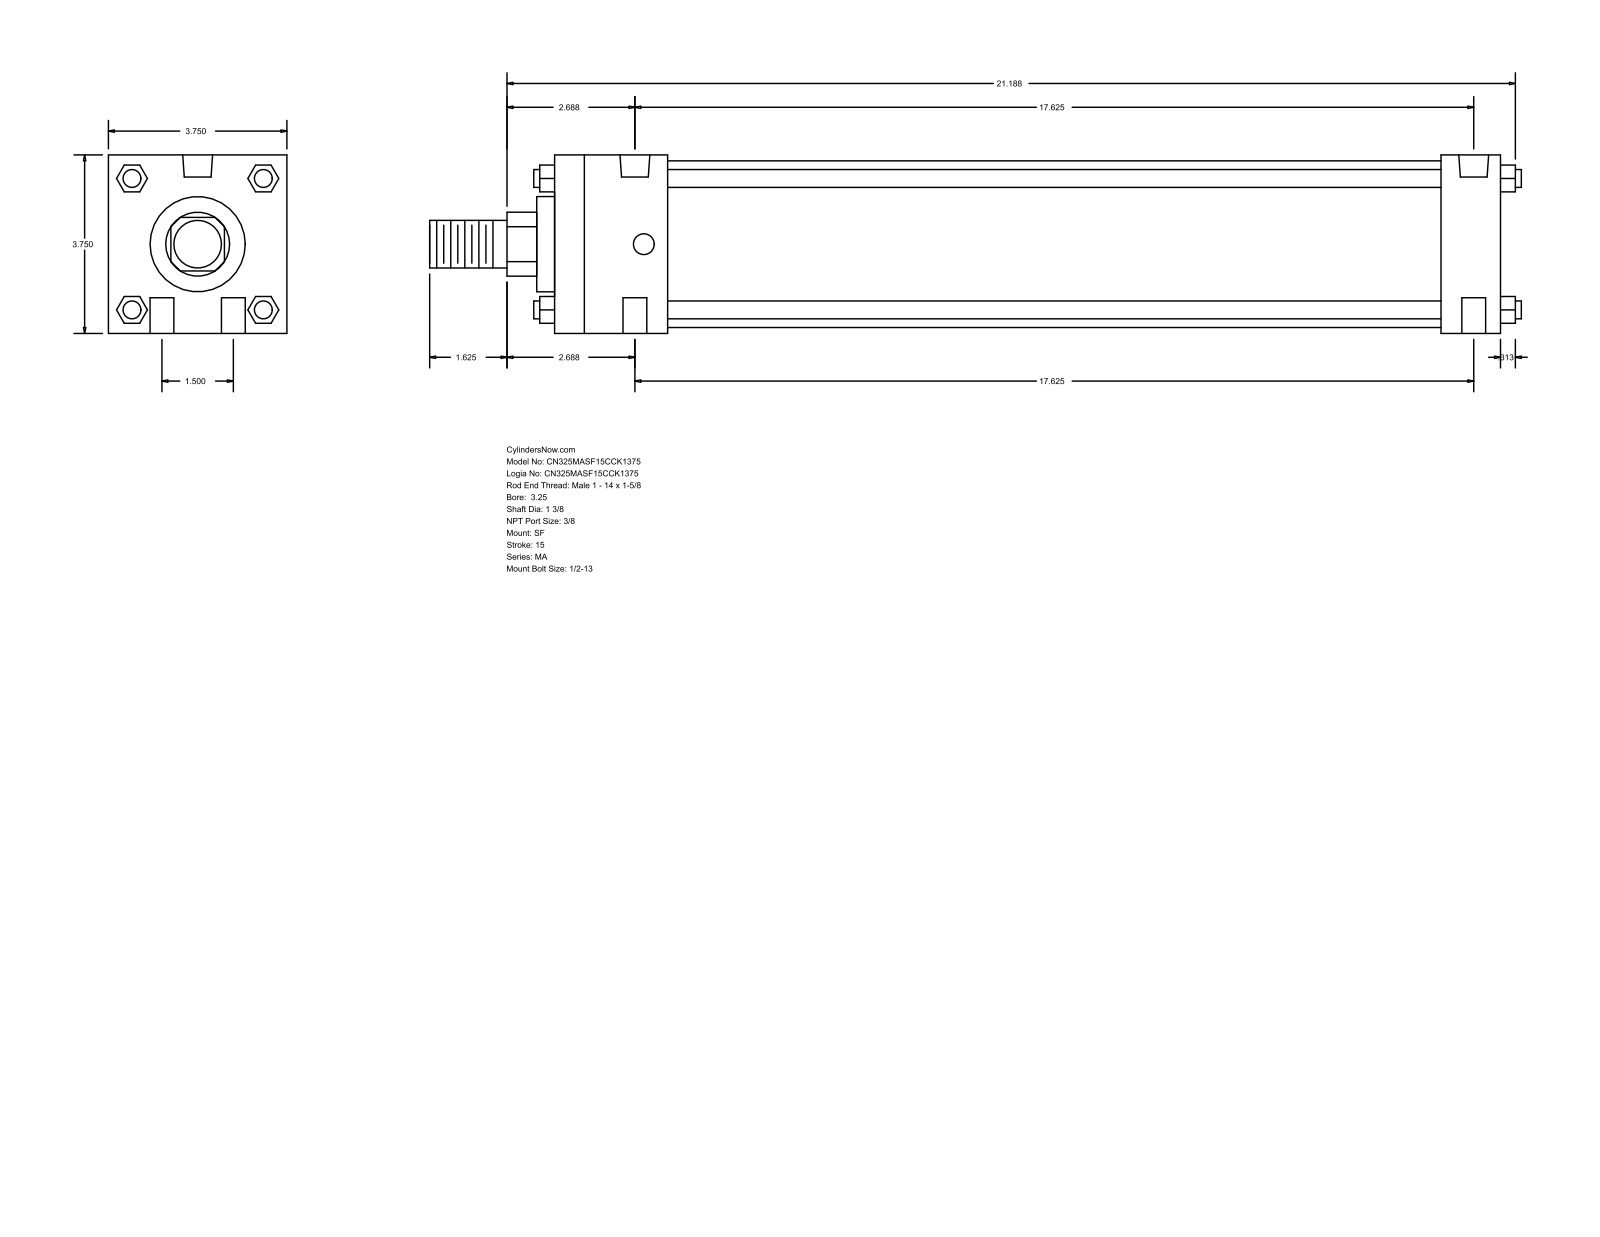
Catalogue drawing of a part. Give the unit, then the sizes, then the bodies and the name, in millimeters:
Units: millimetres
Overall size (bounding box): 582.61 × 95.25 × 95.25
Round holes (diameter × count): ⌀12.7 ×4, ⌀11.11 ×2, ⌀15.93 ×2
Round bosses / shafts (diameter × count): ⌀9.53 ×4, ⌀88.9 ×1, ⌀50.8 ×1, ⌀34.92 ×1, ⌀25.4 ×1
Partial cylindrical surfaces — rounded edges, fillets, slot ends (radius × count): R17.06 ×1
Main face-to-face distances: 95.24, 504.83, 473.08, 31.75, 60.32, 412.76, 444.51, 9.52, 69.84, 482.6
Hole centre spacings: 19.05, 448.09, 447.68, 38.1, 449.3, 438.15
Bodies: 0 solids, 124 faces (94 planar, 30 cylindrical, 0 other)
Part name (STEP PRODUCT): MA_SF__0325_1.375
STEP written by: GSSL Pune (CONFIG_CONTROL_DESIGN)
